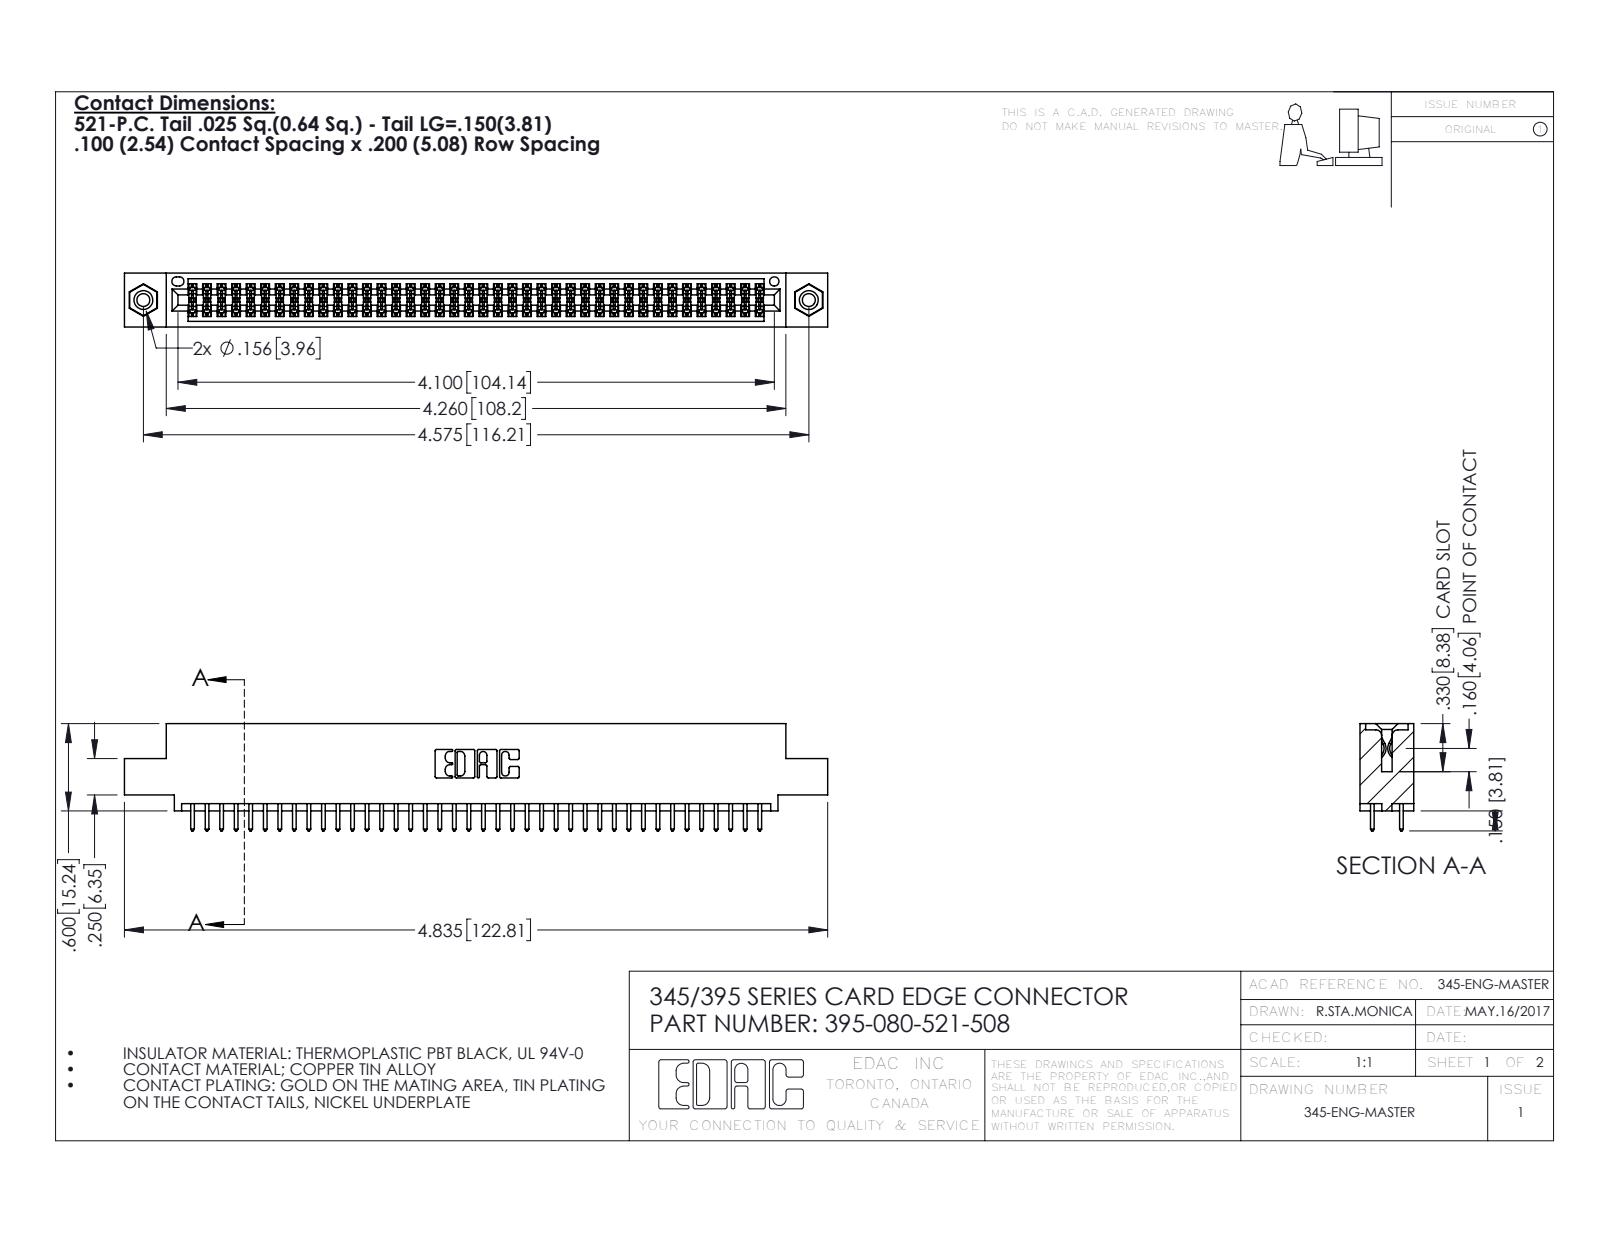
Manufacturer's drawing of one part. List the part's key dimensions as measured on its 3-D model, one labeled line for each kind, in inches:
Part name (STEP PRODUCT): 345-250-001_345-250-003-102; 345 Part_0.110 Offset - 0.156 Dia-TI; 395-080-521-508; 345-292-001_345-293-121
STEP written by: SolidWorks 2016 (CONFIG_CONTROL_DESIGN)
Units: inches
Bodies: 83 solids, 4190 faces (2756 planar, 1418 cylindrical, 16 other)
Overall size (bounding box): 4.835 × 0.737 × 0.37
Volume: 0.72 in³ · Surface area: 26.81 in²
Round holes (diameter × count): ⌀0.089 ×2, ⌀0.125 ×2, ⌀0.156 ×2, ⌀0.064 ×1
Round bosses / shafts (diameter × count): ⌀0.155 ×2
Partial cylindrical surfaces — rounded edges, fillets, slot ends (radius × count): R0.006 ×120, R0.01 ×80, R0.01 ×22, R0.007 ×6, R0.031 ×6, R0.026 ×3, R0.014 ×2, R0.019 ×2
Main face-to-face distances: 0.072, 0.298, 0.2, 0.37, 0.098, 0.272, 0.025, 0.225, 0.175, 0.149
Hole centre spacings: 0.27, 4.339, 4.575
